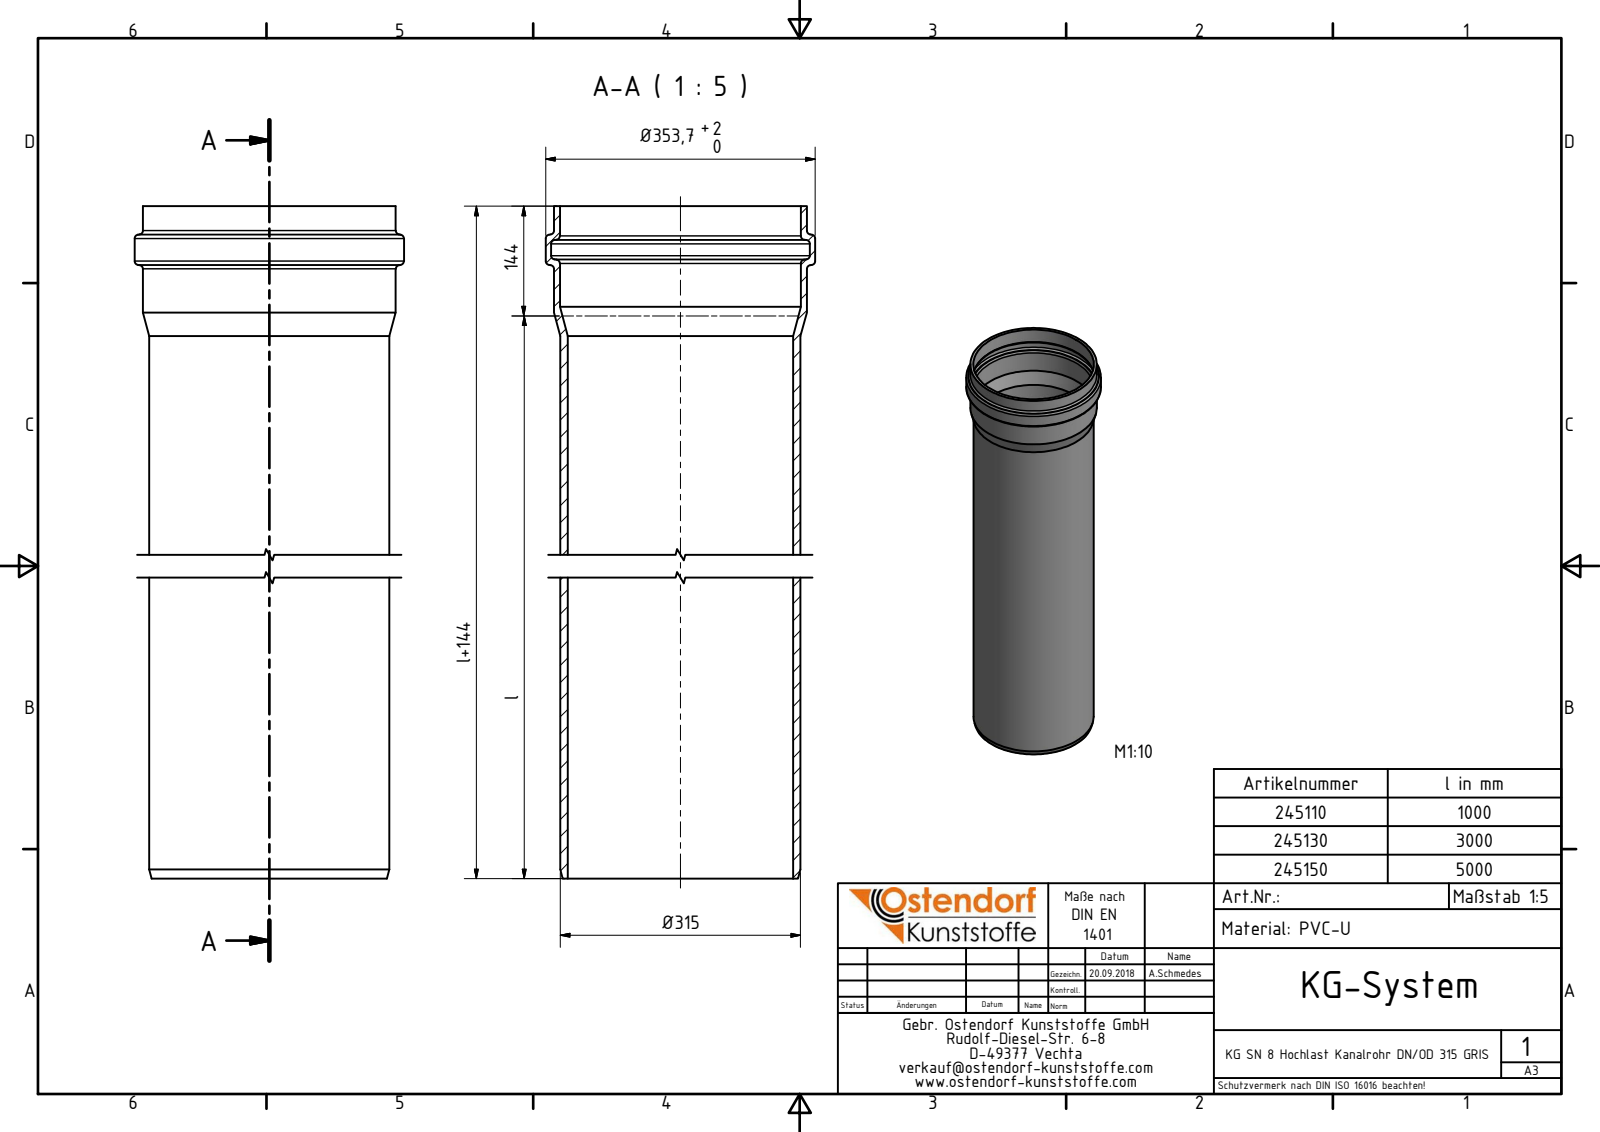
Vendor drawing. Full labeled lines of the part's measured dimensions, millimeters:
Part name (STEP PRODUCT): 245110 KGEM Passlängen SN 8 DN_OD 315x1000 GRIS
STEP written by: Autodesk Inventor 2016 (AUTOMOTIVE_DESIGN)
Units: millimetres
Bodies: 1 solid, 25 faces (2 planar, 8 cylindrical, 15 other)
Overall size (bounding box): 1144 × 353.7 × 353.7
Volume: 10 710 000 mm³ · Surface area: 2 264 000 mm²
Round holes (diameter × count): ⌀295.7 ×1, ⌀316.35 ×1, ⌀339.9 ×1
Round bosses / shafts (diameter × count): ⌀353.7 ×1, ⌀331.95 ×1, ⌀315.3 ×1
Main face-to-face distances: 1144
